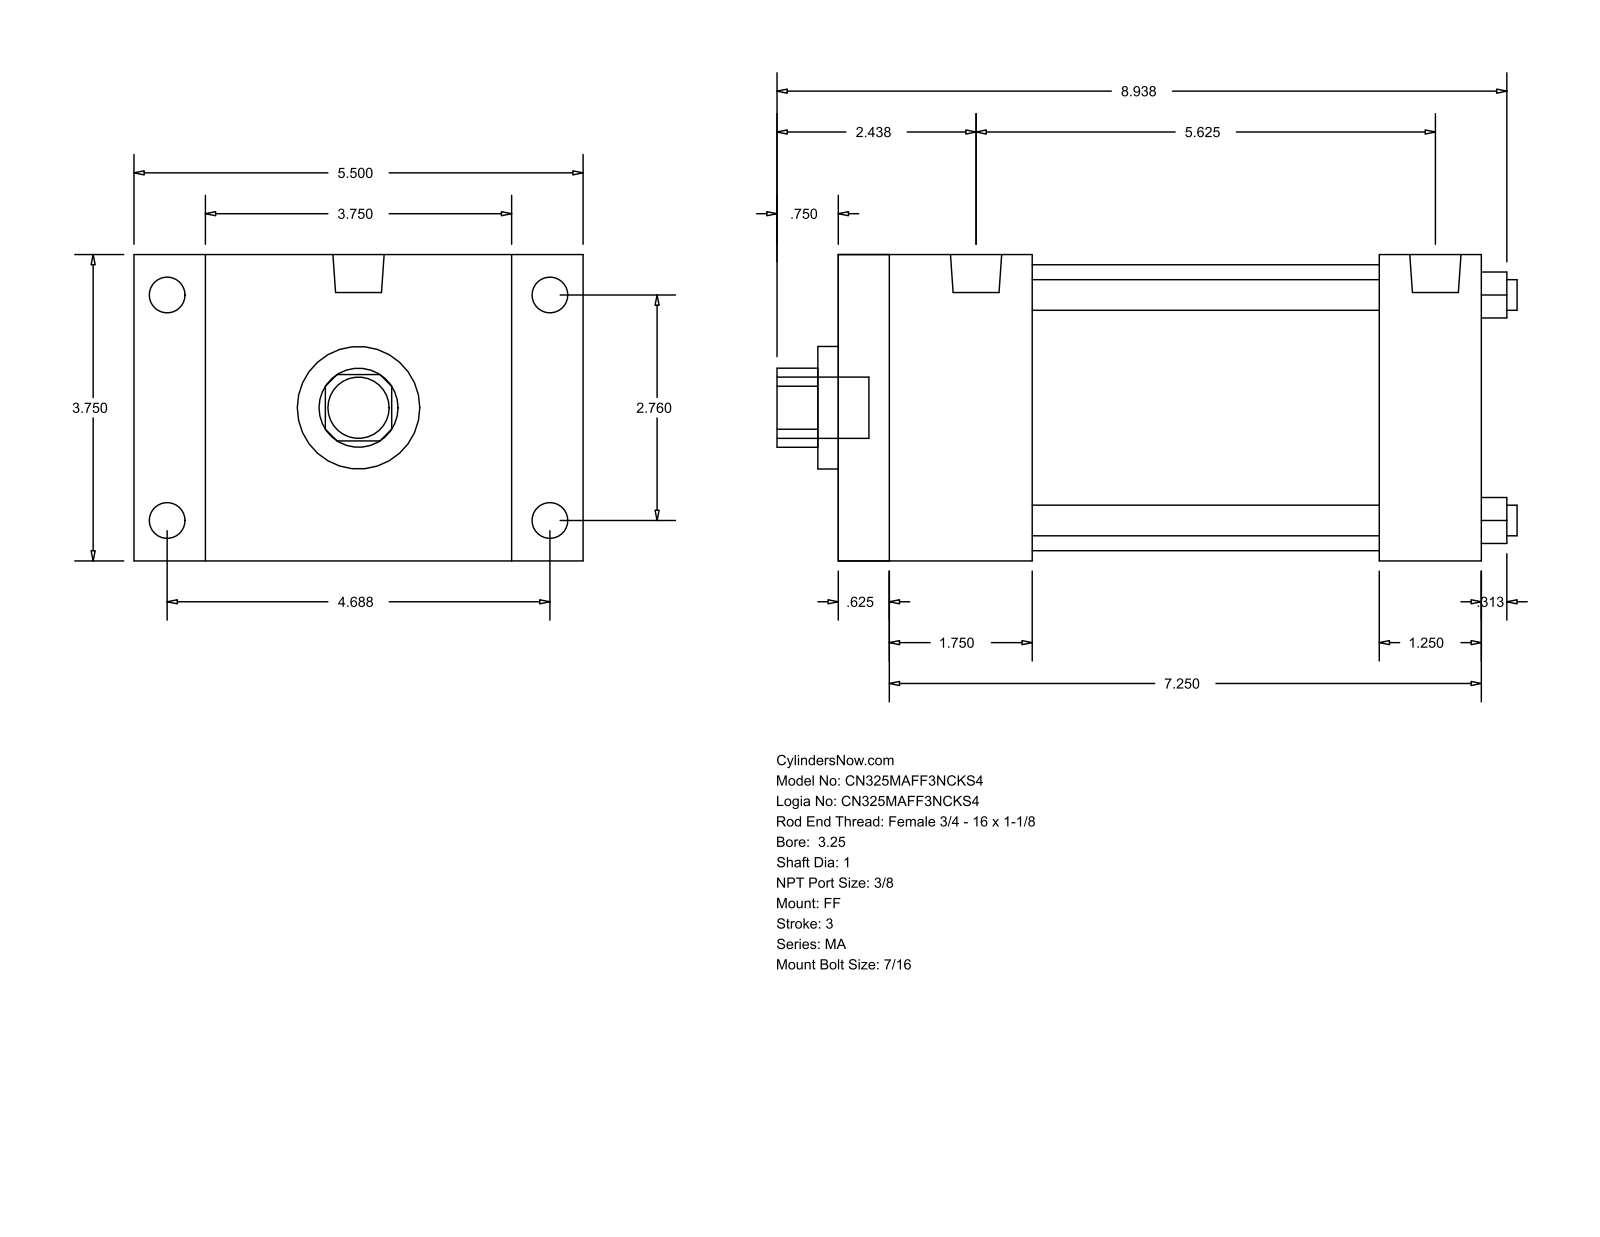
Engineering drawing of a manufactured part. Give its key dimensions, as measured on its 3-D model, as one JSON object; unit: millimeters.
{"part_name": "MA_FF__0325_1", "step_written_by": "GSSL Pune (CONFIG_CONTROL_DESIGN)", "units": "millimeters", "bodies": {"solids": 0, "faces": 92, "planar": 64, "cylindrical": 28, "other": 0}, "overall_size": [230.19, 139.7, 95.25], "round_holes": [[9.53, 4], [25.4, 1], [38.1, 1], [88.9, 1]], "round_bosses_or_shafts": [[11.11, 8], [15.93, 2], [19.05, 1]], "partial_cylinders_radius": [[12.29, 1]], "face_to_face_distances": [95.24, 200.02, 15.87, 184.15, 22.23, 117.47, 60.33, 168.27, 44.46, 152.4], "hole_center_spacings": [49.57, 70.1, 99.14]}
